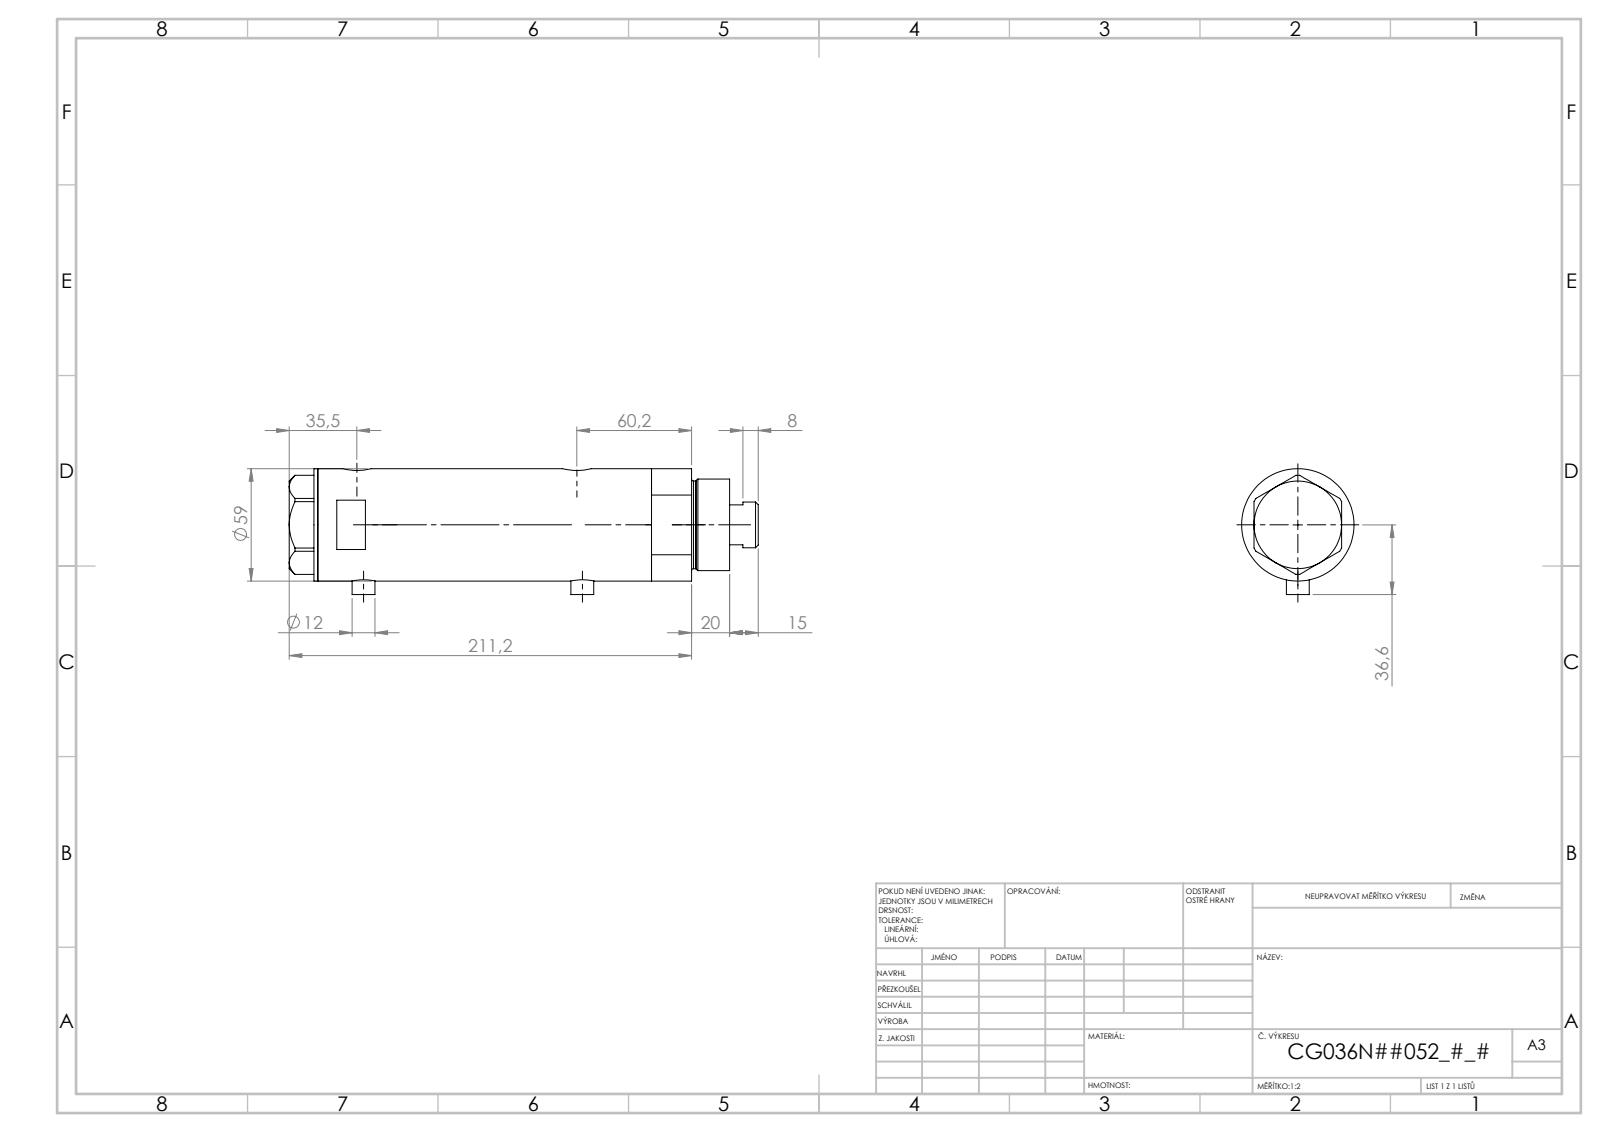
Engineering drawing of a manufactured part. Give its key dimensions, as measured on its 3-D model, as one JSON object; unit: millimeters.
{"part_name": "V270CG_FRONT; V270CG_MIDDLE; V270CG_VC; V270CG_BACK", "step_written_by": "SolidWorks 2019 (CONFIG_CONTROL_DESIGN)", "units": "millimeters", "bodies": {"solids": 4, "faces": 120, "planar": 51, "cylindrical": 49, "other": 20}, "overall_size": [246.2, 66.1, 59], "volume_mm3": 573079, "surface_area_mm2": 114310, "round_holes": [[9.73, 2], [12.5, 2], [15, 2], [8.5, 1], [25, 1], [26.5, 1], [36, 1], [40, 1], [52, 1]], "round_bosses_or_shafts": [[12, 2], [59, 1], [48, 1], [46, 1], [24, 1]], "face_to_face_distances": [137.2, 23.5, 113.7, 15, 38.5, 152.2, 2, 231.2, 216.2, 192.7], "hole_center_spacings": [2.9, 3.5, 112, 114.9, 115.5, 118.4]}
